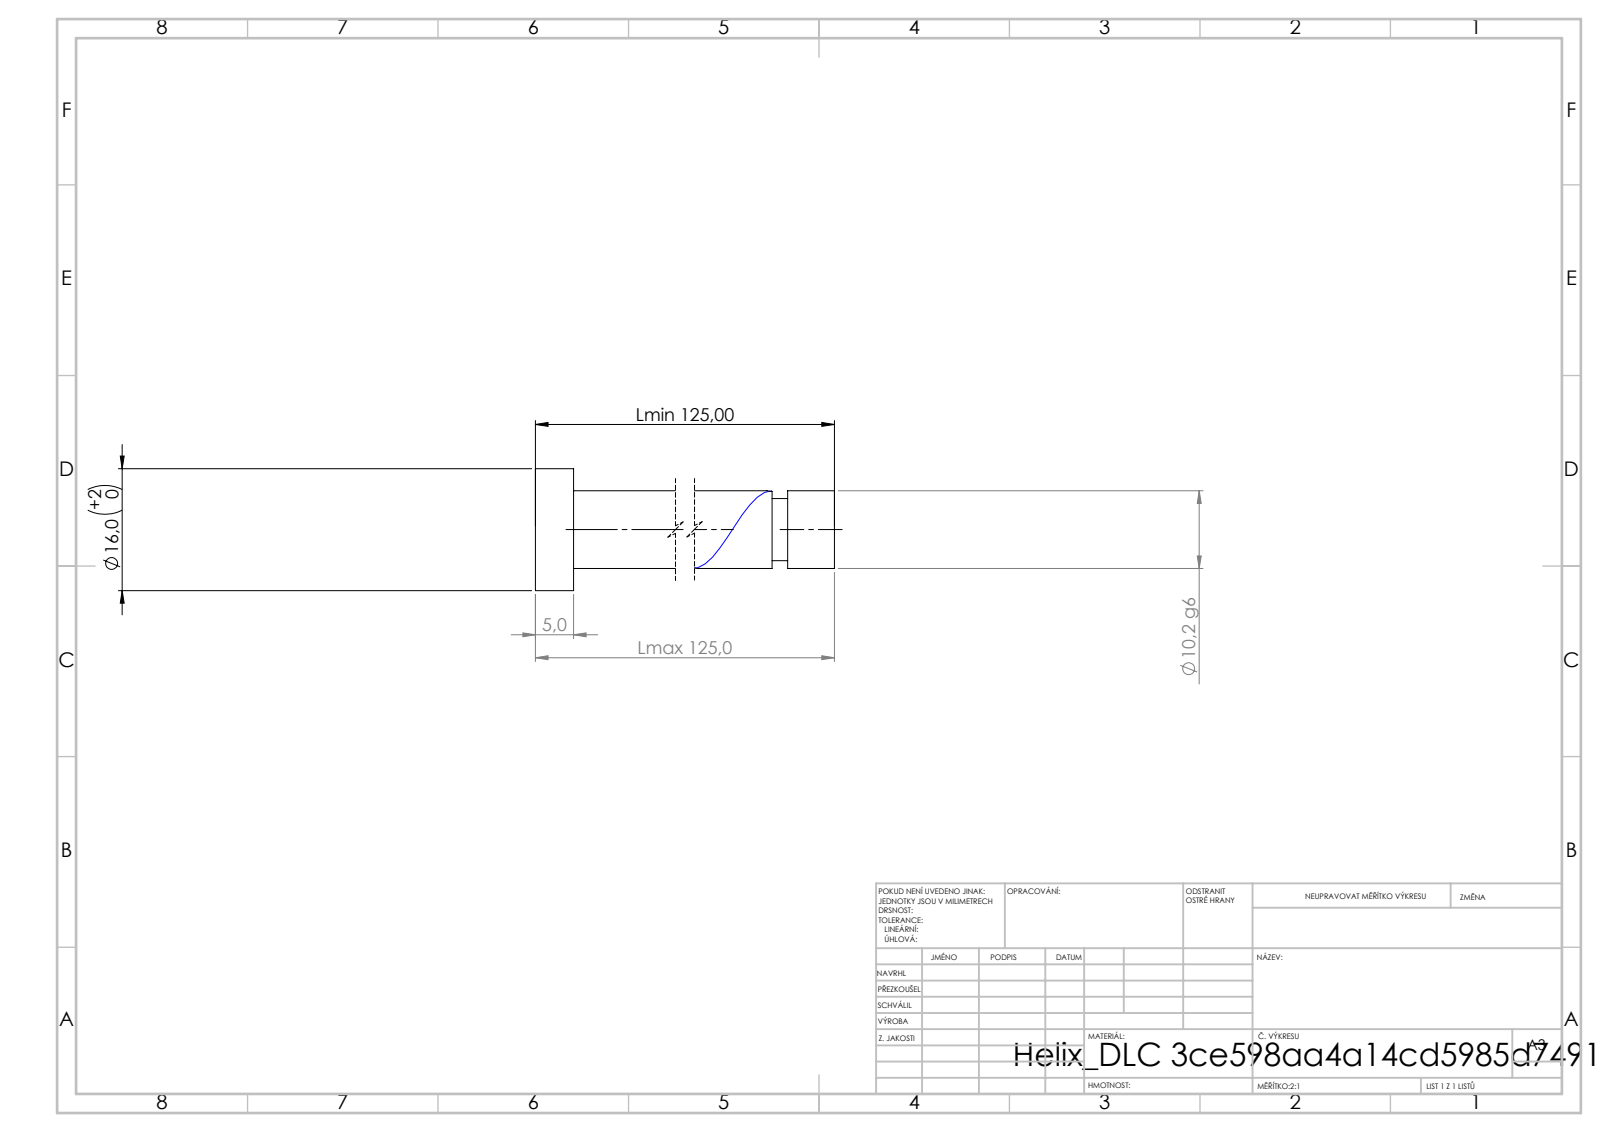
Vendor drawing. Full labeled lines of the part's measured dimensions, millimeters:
STEP written by: SolidWorks 2019 (CONFIG_CONTROL_DESIGN)
Units: millimetres
Bodies: 1 solid, 21 faces (6 planar, 14 cylindrical, 1 other)
Overall size (bounding box): 125 × 16 × 16
Volume: 10 653 mm³ · Surface area: 4 683 mm²
Round bosses / shafts (diameter × count): ⌀16 ×1, ⌀10.2 ×1, ⌀8.16 ×1
Main face-to-face distances: 5, 125, 120, 118.85, 113.85, 6.15, 116.81, 111.81, 2.04, 8.19
